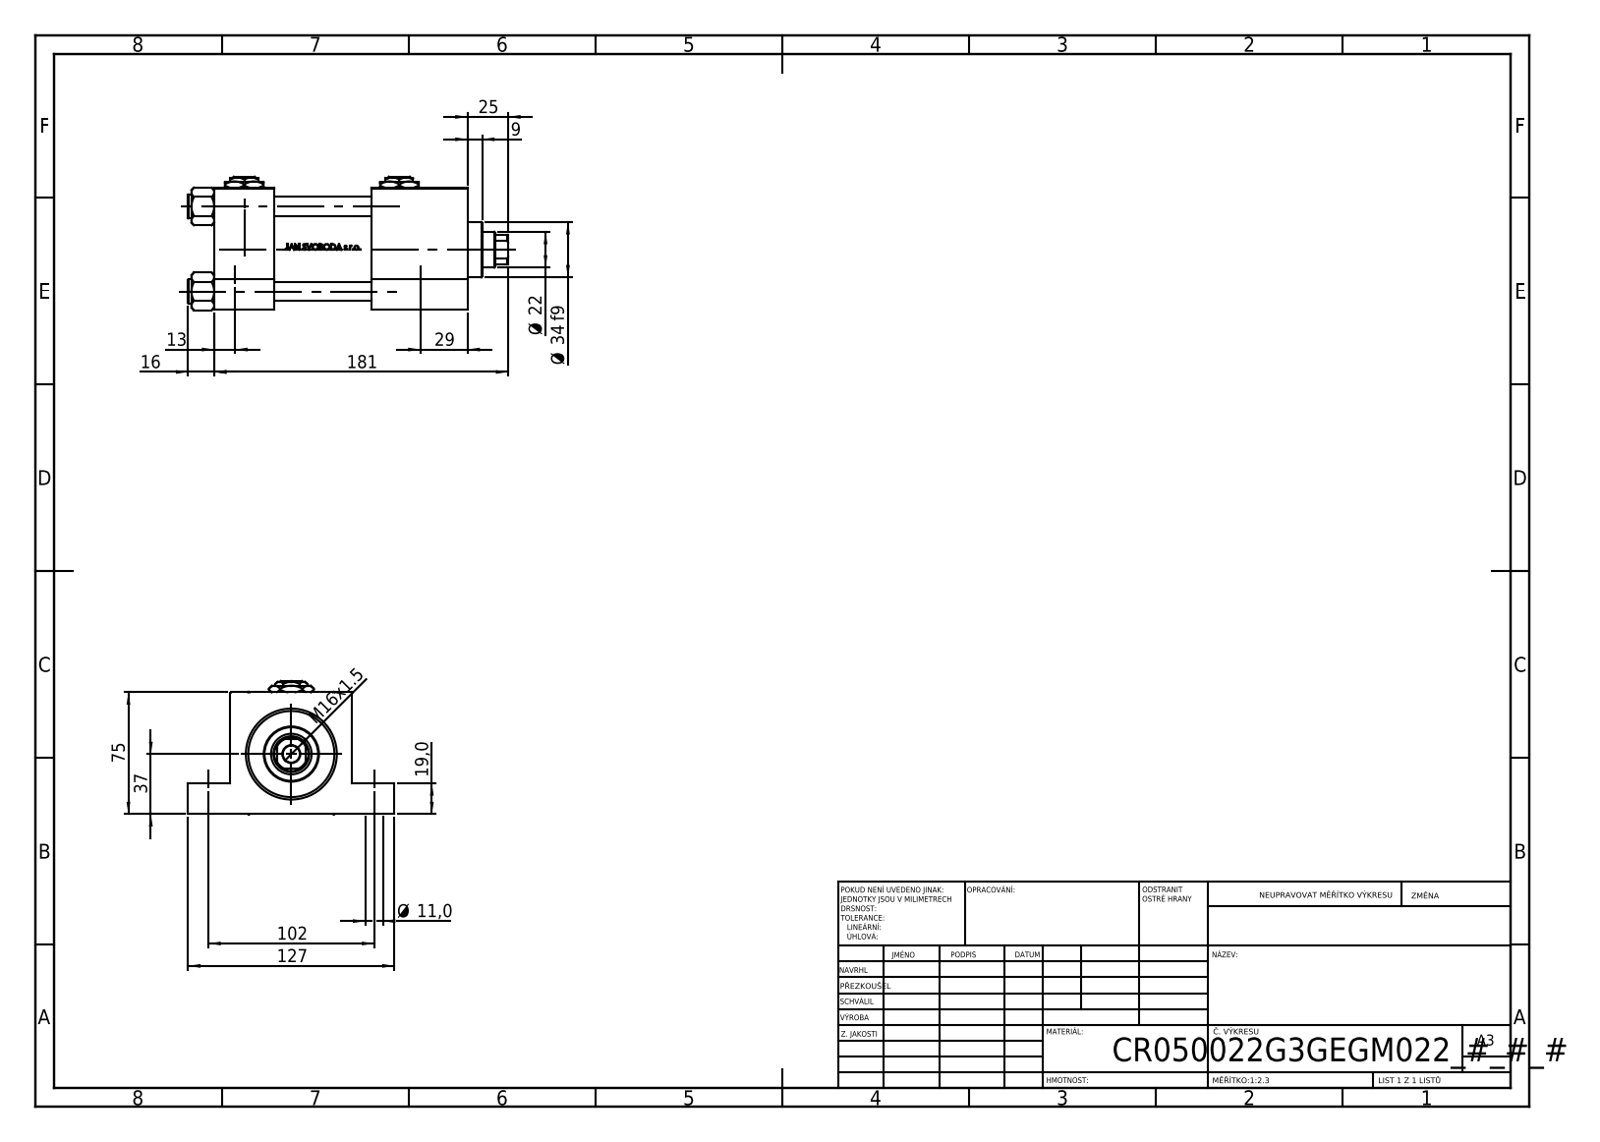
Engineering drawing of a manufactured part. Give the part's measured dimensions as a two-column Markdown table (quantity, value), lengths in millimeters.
| quantity | value |
| --- | --- |
| part name | V215_VC_A; NUT_M5_G; Zatka_pro_OIL_PORT; V215CR_VCP_G (+2 more) |
| STEP written by | SolidWorks 2019 (CONFIG_CONTROL_DESIGN) |
| units | millimeters |
| bodies | 13 solids, 1172 faces (476 planar, 124 cylindrical, 572 other) |
| overall size | 197 × 127 × 82.27 |
| volume | 763 888 mm³ |
| surface area | 163 398 mm² |
| round holes (diameter × count) | 11 × 4, 12 × 4, 7 × 2, 20.96 × 2, 30 × 2, 10.5 × 1, 22 × 1, 25 × 1, 41 × 1, 50 × 1, 53 × 1 |
| round bosses / shafts (diameter × count) | 15 × 4, 56 × 1, 34 × 1 |
| partial cylindrical surfaces (radius × count) | 10.5 × 1 |
| main face-to-face distances | 75, 37, 156, 119, 19, 56, 97, 60, 59, 26 |
| hole center spacings | 52.3, 36.63, 37.34, 51.3, 52.63, 73.96, 102, 113.15 |
